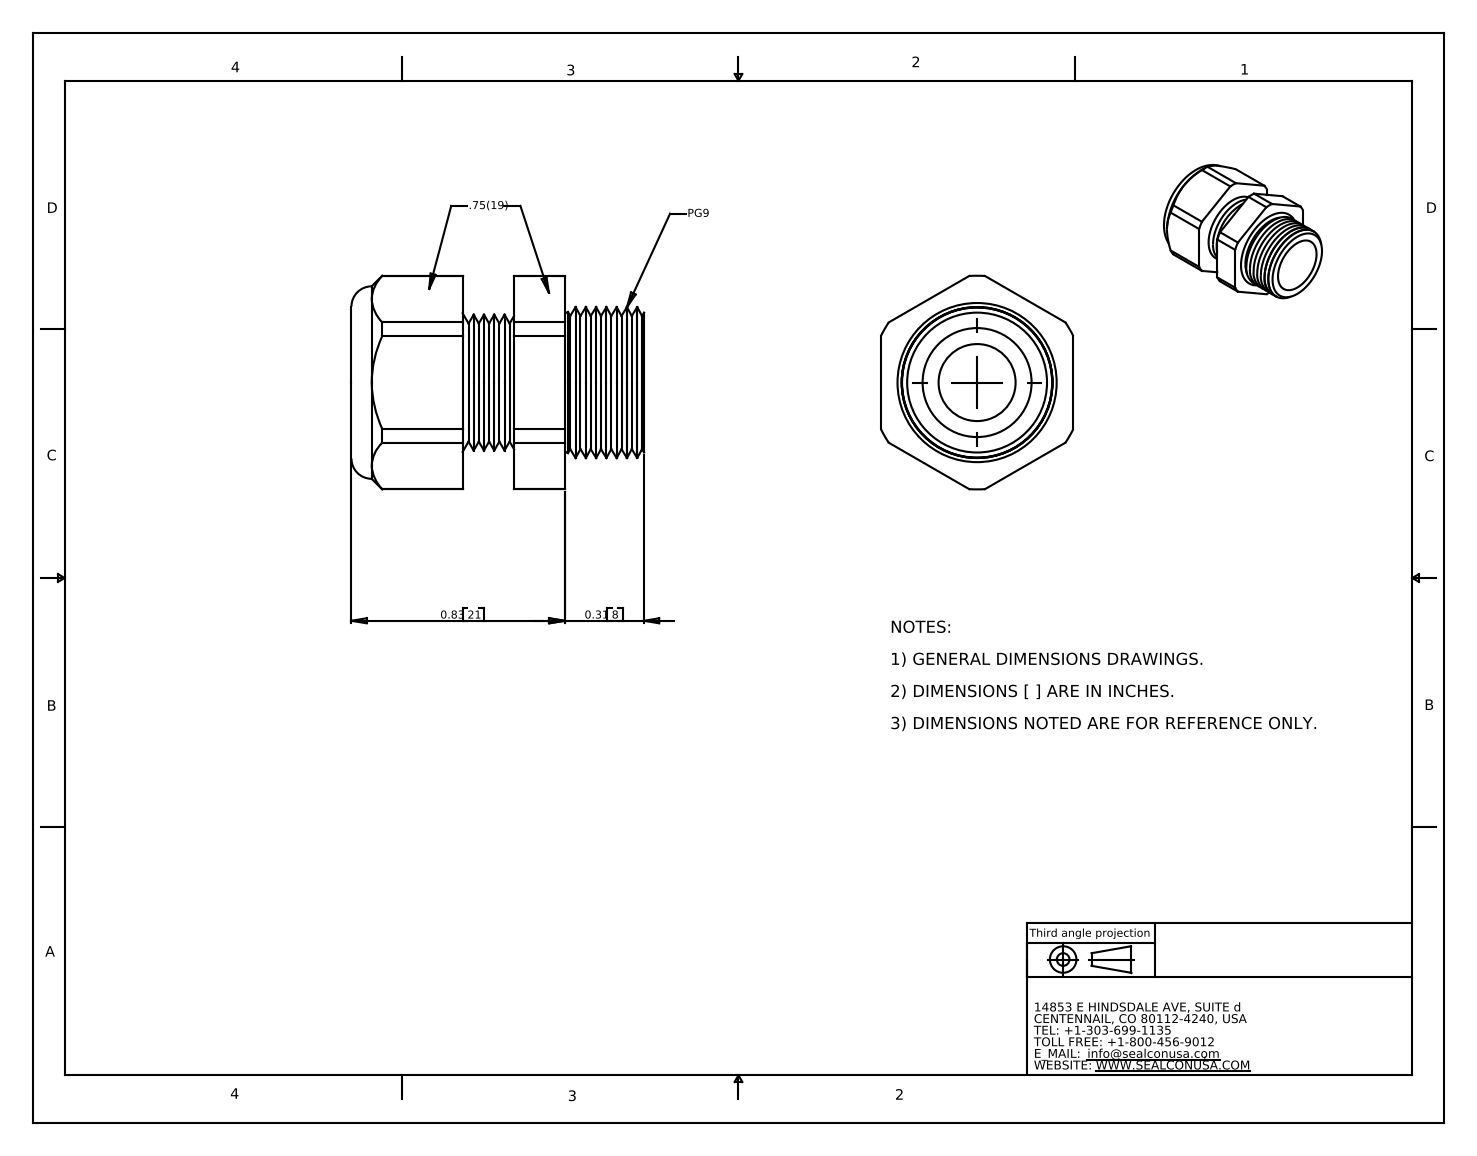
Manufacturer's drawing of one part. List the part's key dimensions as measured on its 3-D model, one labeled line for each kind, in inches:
Part name (STEP PRODUCT): CD09BA-BK
STEP written by: SolidWorks 2007 (CONFIG_CONTROL_DESIGN)
Units: inches
Bodies: 2 solids, 114 faces (20 planar, 22 cylindrical, 72 other)
Overall size (bounding box): 1.14 × 0.833 × 0.75
Volume: 0.309 in³ · Surface area: 7.115 in²
Round holes (diameter × count): ⌀0.3 ×1, ⌀0.48 ×1, ⌀0.54 ×1
Partial cylindrical surfaces — rounded edges, fillets, slot ends (radius × count): R0.416 ×1
Main face-to-face distances: 0.75, 0.2, 0.75, 0.397, 0.197, 0.403, 0.603, 0.8, 0.03, 0.433
